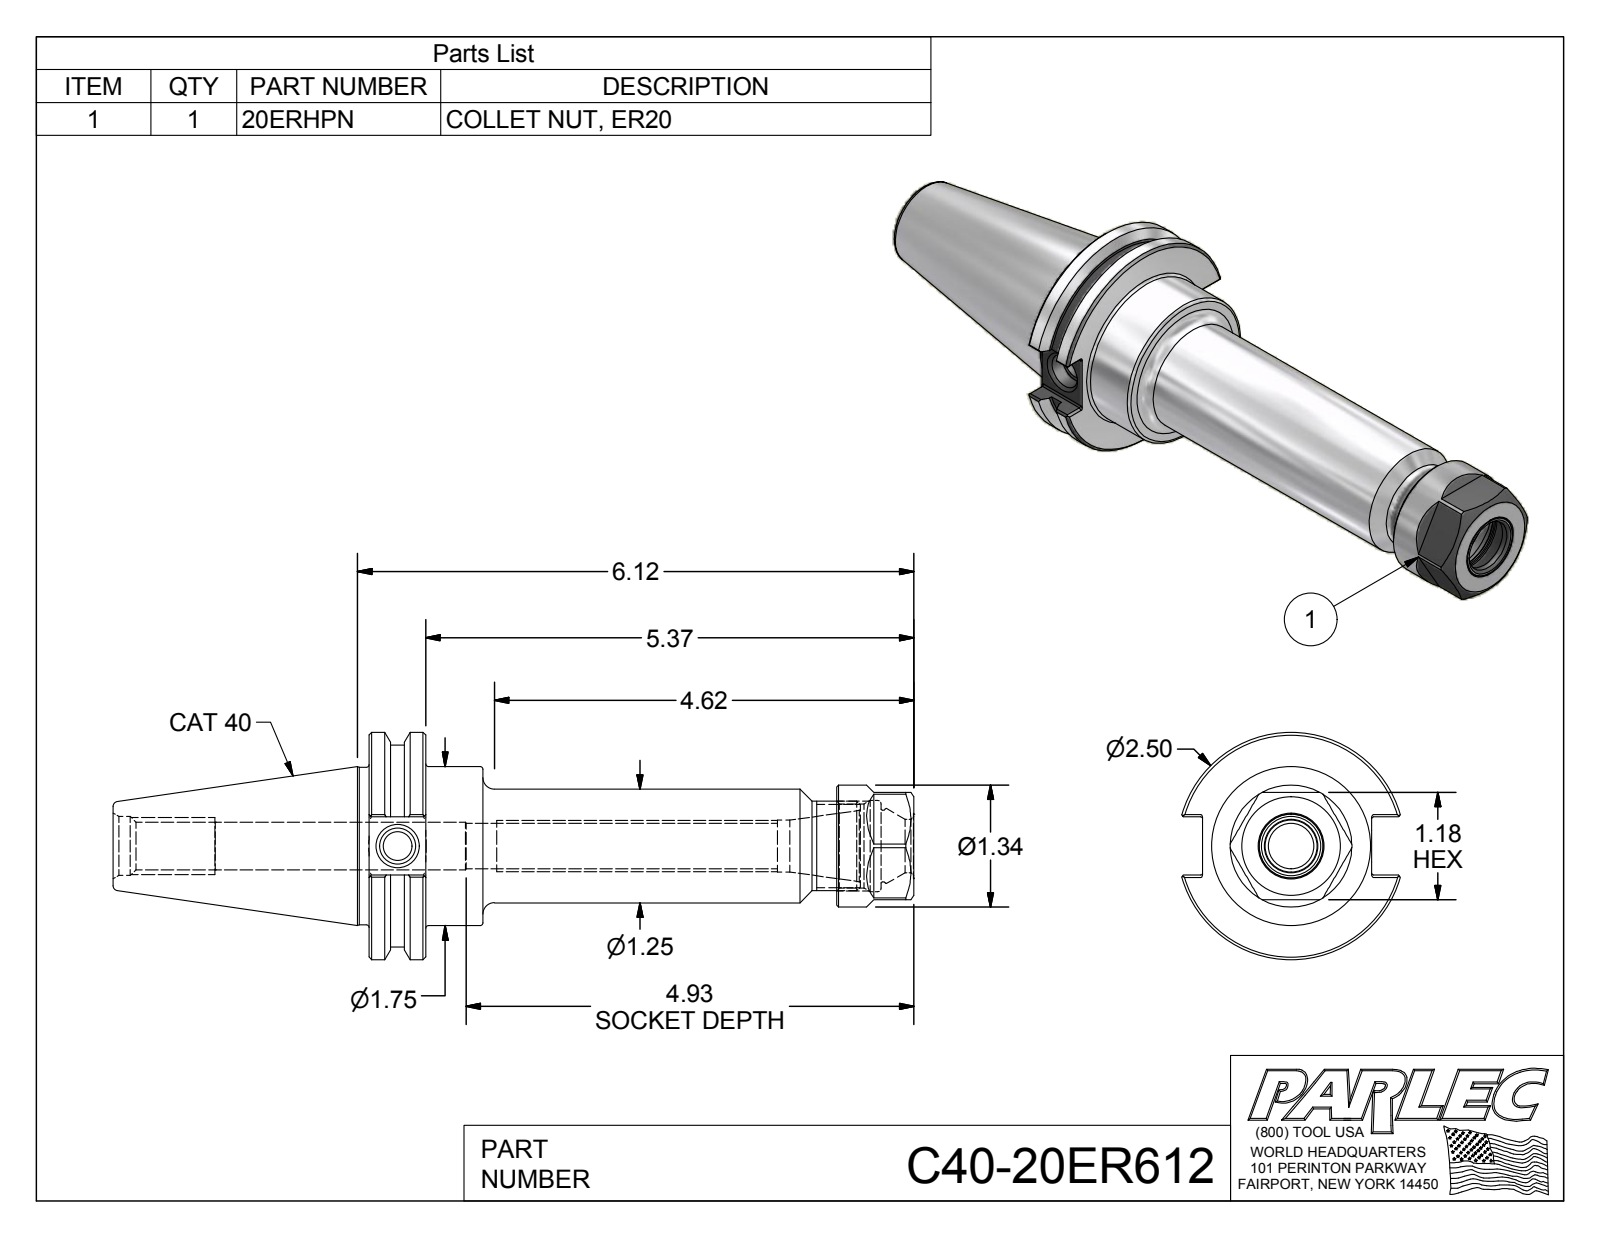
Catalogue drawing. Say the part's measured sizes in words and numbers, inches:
The part is named "C40-20ER612; C40-20ER6-1; 20ERHPN". Its 3-D file was written by "Autodesk Inventor 2012 (AUTOMOTIVE_DESIGN)". It is 2 solids with 120 faces: 49 planar, 34 cylindrical and 37 other. Overall it measures 8.808 by 2.5 by 2.403 inches. Its volume is 11.98 cubic inches and its surface area 65.28 square inches. Round holes: 1 of diameter 0.315, 1 of diameter 0.399, 1 of diameter 0.502, 1 of diameter 0.526, 1 of diameter 0.527, 1 of diameter 0.57, 1 of diameter 0.587, 1 of diameter 0.648, 1 of diameter 0.79, 1 of diameter 0.926, 1 of diameter 1.005. Round bosses or shafts: 1 of diameter 2.5, 1 of diameter 2.219, 1 of diameter 1.75, 1 of diameter 1.73, 1 of diameter 1.34, 1 of diameter 1.25, 1 of diameter 0.984. Partial cylindrical surfaces (rounded edges, fillets, slot ends): 12 of radius 0.02. The main face-to-face distances are 0.625, 1.18, 5.145, 4.52, 5.995, 5.37, 0.85, 1.255, 0.63, 3.89.
